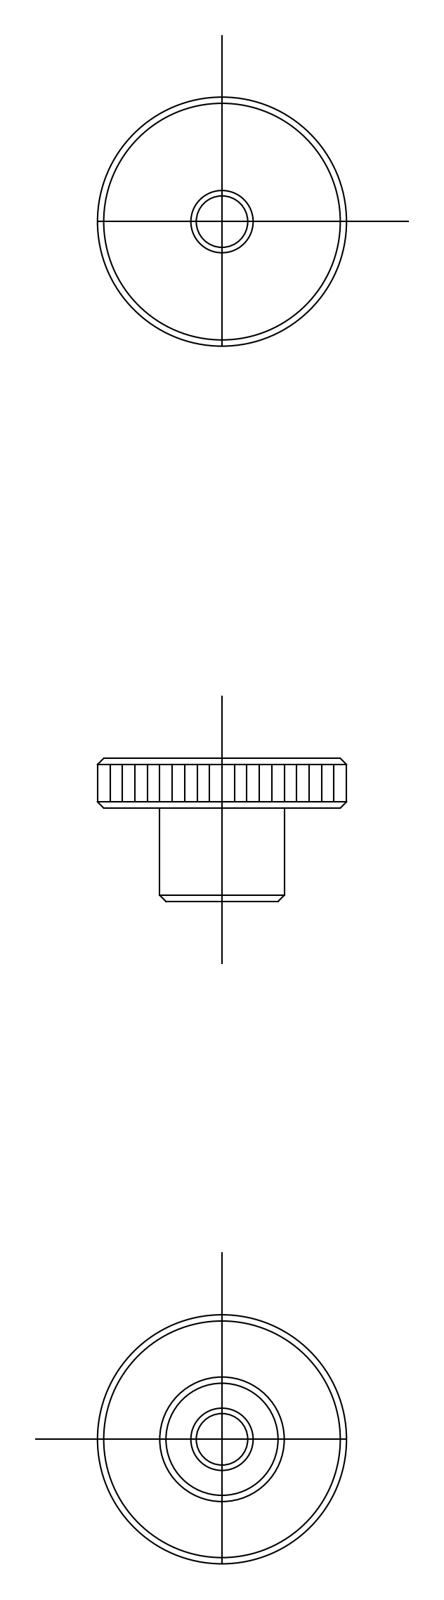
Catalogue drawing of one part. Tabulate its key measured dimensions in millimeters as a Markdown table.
| quantity | value |
| --- | --- |
| part name | knob |
| STEP written by | CADfix (AUTOMOTIVE_DESIGN) |
| units | millimeters |
| bodies | 1 solid, 15 faces (0 planar, 0 cylindrical, 15 other) |
| overall size | 20 × 20 × 11.5 |
| volume | 1 603 mm³ |
| surface area | 1 210 mm² |
